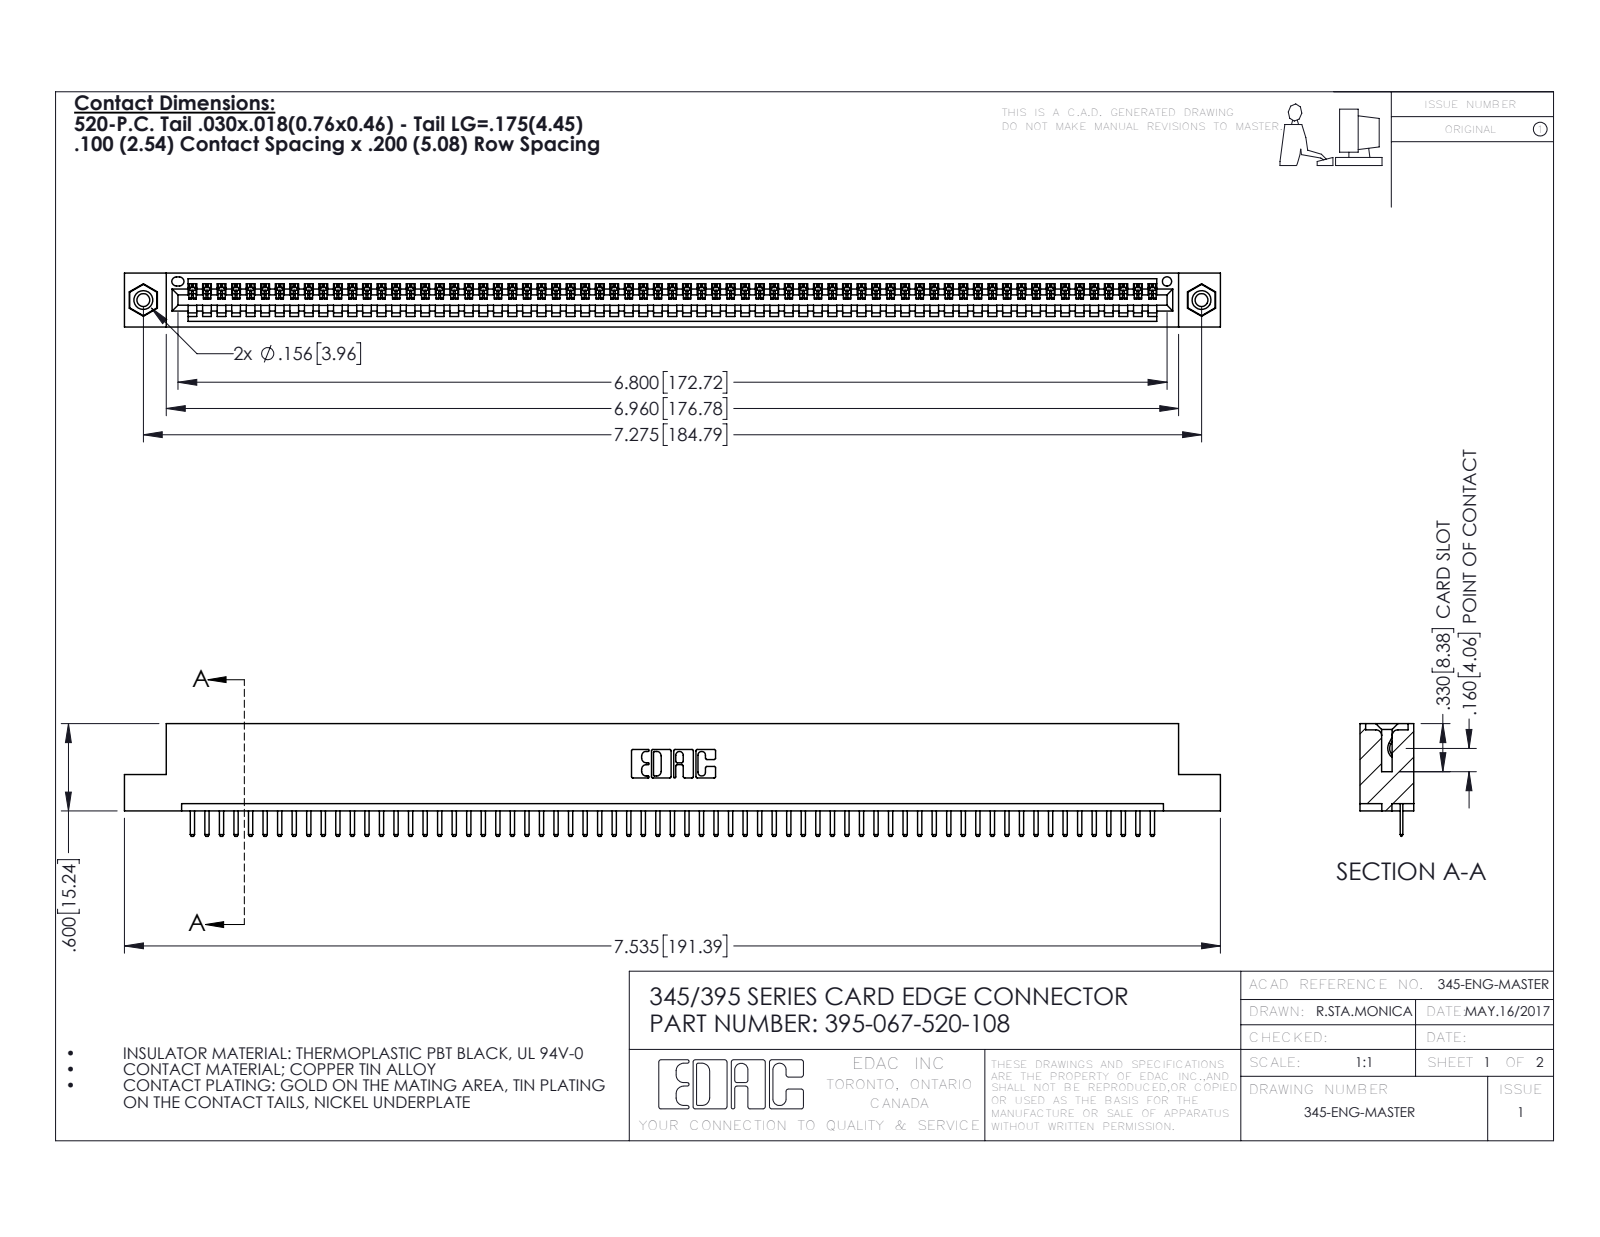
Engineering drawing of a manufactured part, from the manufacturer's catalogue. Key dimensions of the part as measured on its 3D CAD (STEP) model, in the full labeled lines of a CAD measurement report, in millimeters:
Part name (STEP PRODUCT): 345-250-001_345-250-003-102; 395-067-520-108; 345-292-001_345-293-120; 345 Part_Flush Mounting Lugs - 0.156 Dia-TI
STEP written by: SolidWorks 2016 (CONFIG_CONTROL_DESIGN)
Units: millimetres
Bodies: 70 solids, 4340 faces (2926 planar, 1398 cylindrical, 16 other)
Overall size (bounding box): 191.4 × 19.7 × 9.4
Volume: 18 190 mm³ · Surface area: 23 890 mm²
Round holes (diameter × count): ⌀2.3 ×2, ⌀3.2 ×2, ⌀4 ×2, ⌀1.6 ×1
Round bosses / shafts (diameter × count): ⌀3.9 ×2
Partial cylindrical surfaces — rounded edges, fillets, slot ends (radius × count): R0.3 ×136, R0.2 ×134, R0.3 ×22, R0.2 ×6, R0.8 ×6, R0.7 ×3, R0.8 ×2, R1 ×2
Main face-to-face distances: 1.8, 7.6, 9.4, 5.1, 2.5, 6.9, 0.6, 5.7, 1.8, 3.8
Hole centre spacings: 6.9, 178.8, 184.8
